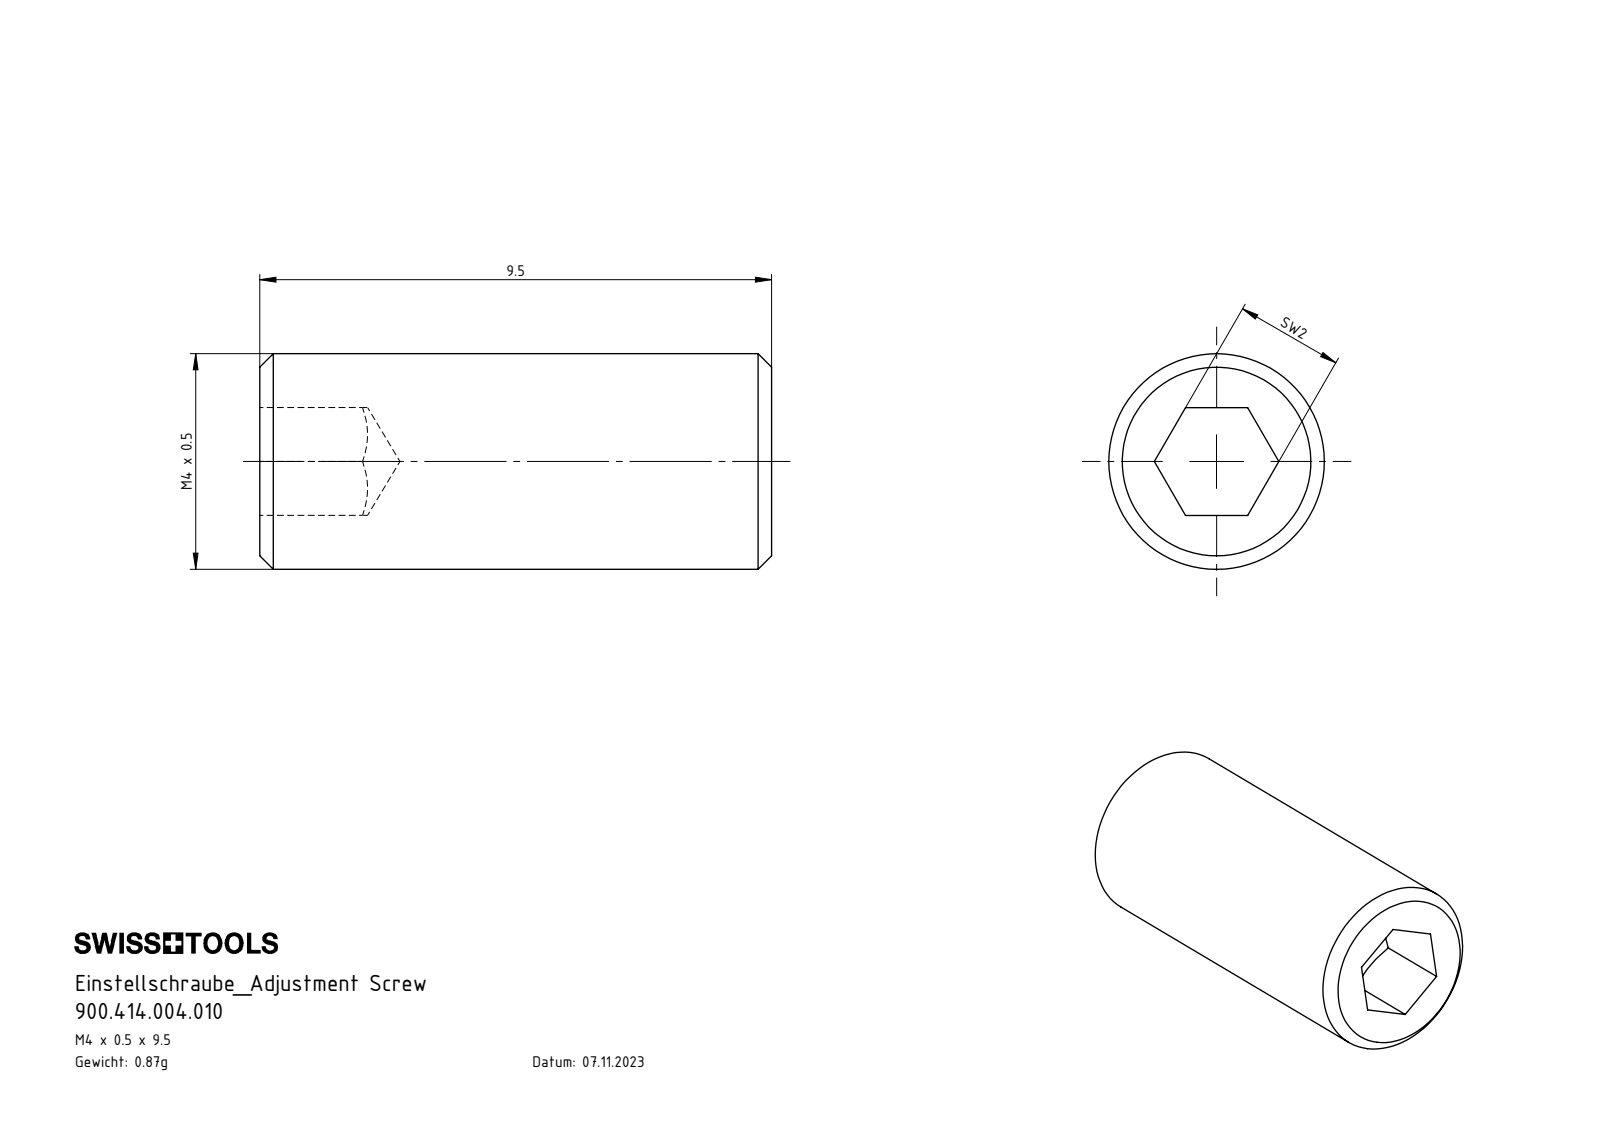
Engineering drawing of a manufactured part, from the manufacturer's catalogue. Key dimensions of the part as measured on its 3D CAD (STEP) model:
Part name (STEP PRODUCT): 900.414.004.010
STEP written by: SolidWorks 2022 (AUTOMOTIVE_DESIGN)
Units: millimetres
Bodies: 1 solid, 16 faces (8 planar, 2 cylindrical, 6 other)
Overall size (bounding box): 9.5 × 4 × 4
Volume: 111 mm³ · Surface area: 155 mm²
Round bosses / shafts (diameter × count): ⌀4 ×1
Main face-to-face distances: 2, 9.5
